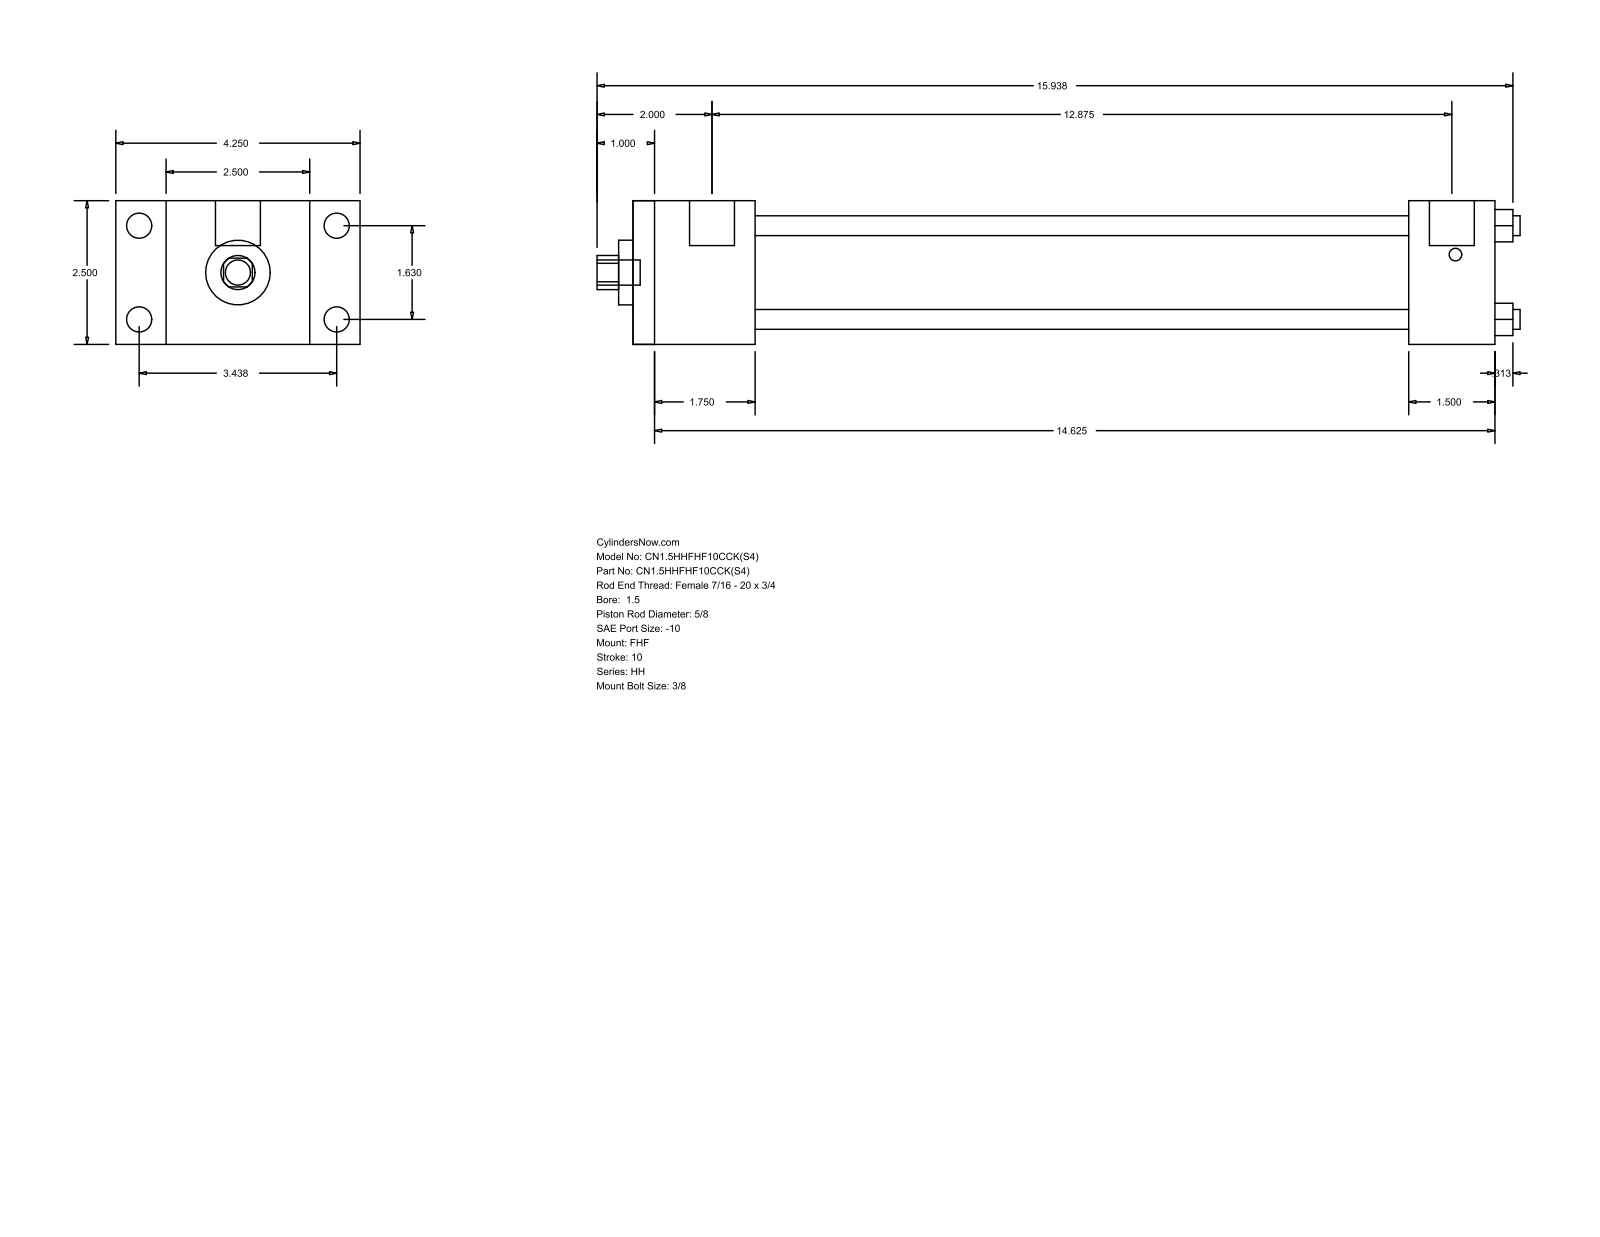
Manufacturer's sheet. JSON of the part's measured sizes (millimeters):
{"part_name": "HH_FHF__0150_0.625", "step_written_by": "GSSL Pune (CONFIG_CONTROL_DESIGN)", "units": "millimeters", "bodies": {"solids": 0, "faces": 88, "planar": 60, "cylindrical": 28, "other": 0}, "overall_size": [407.99, 107.95, 63.5], "round_holes": [[8.76, 4], [15.88, 1], [28.57, 1], [44.45, 1]], "round_bosses_or_shafts": [[11.13, 4], [5.56, 4], [19.84, 2], [11.11, 1]], "partial_cylinders_radius": [[7.54, 1]], "face_to_face_distances": [63.5, 22.23, 85.73, 53.97, 107.96, 381, 327.03, 342.89, 288.92, 38.11], "hole_center_spacings": [29.27, 41.4, 58.55]}
